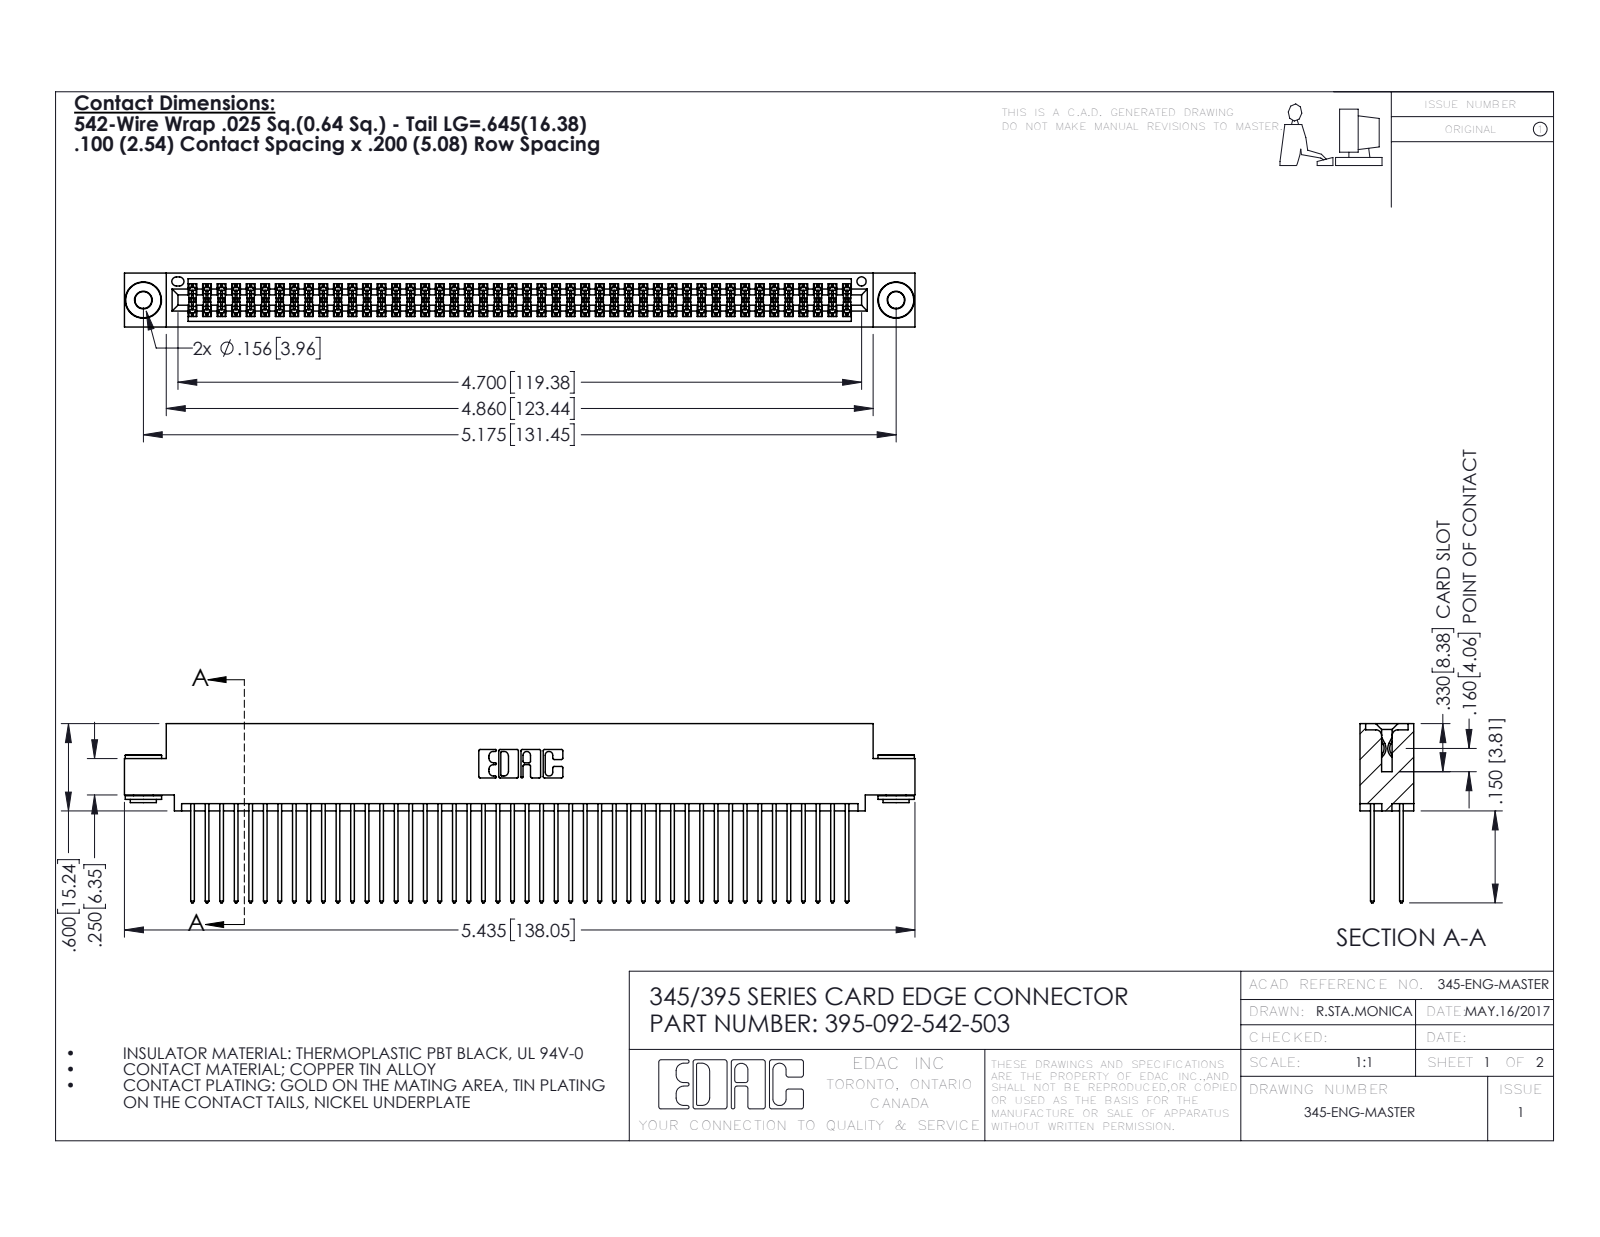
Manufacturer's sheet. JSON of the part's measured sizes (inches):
{"part_name": "345-250-002_345-250-002-102; 395-092-542-503; 345-292-001_345-293-142; 345 Part_0.110 Offset - 0.156 Dia-TH", "step_written_by": "SolidWorks 2016 (CONFIG_CONTROL_DESIGN)", "units": "inches", "bodies": {"solids": 95, "faces": 4768, "planar": 3130, "cylindrical": 1630, "other": 8}, "overall_size": [5.435, 1.232, 0.37], "volume_in3": 0.843, "surface_area_in2": 35.36, "round_holes": [[0.116, 2], [0.156, 2], [0.064, 1]], "round_bosses_or_shafts": [[0.25, 2], [0.18, 2], [0.136, 2]], "partial_cylinders_radius": [[0.006, 138], [0.01, 92], [0.01, 22], [0.007, 6], [0.031, 6], [0.026, 3], [0.014, 2], [0.019, 2]], "face_to_face_distances": [0.072, 0.298, 0.2, 0.025, 0.098, 0.272, 0.225, 0.37, 0.175, 0.149], "hole_center_spacings": [0.27, 4.939, 5.175]}
